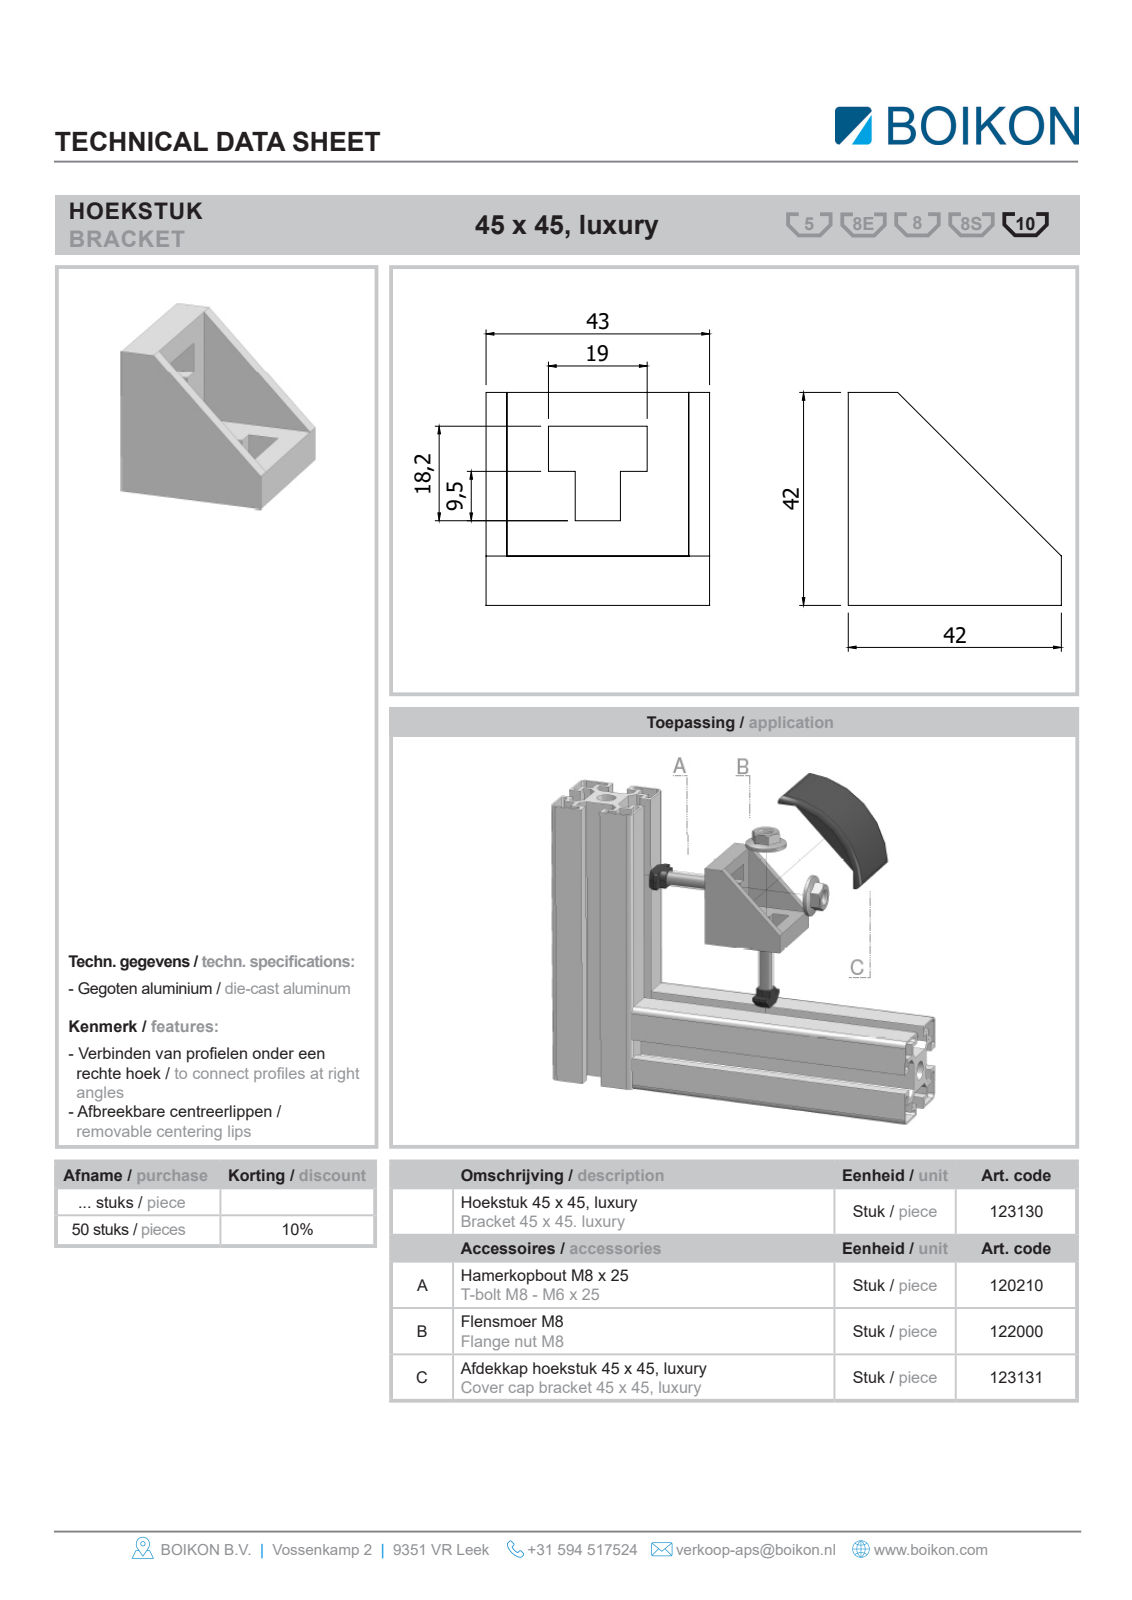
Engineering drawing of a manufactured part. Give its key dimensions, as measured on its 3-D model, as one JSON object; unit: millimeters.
{"part_name": "Root; 123130HOEKSTUK 45x45 LUXURYBOIKON0; 122000Flensmoer M8BOIKON; 120210Hamerkopbout M8x25BOIKON (+1 more)", "step_written_by": "HiCAD 2013 1802.4 Build 509 (AUTOMOTIVE_DESIGN)", "units": "millimeters", "bodies": {"solids": 6, "faces": 214, "planar": 161, "cylindrical": 29, "other": 24}, "overall_size": [56.59, 56.59, 43], "volume_mm3": 51750, "surface_area_mm2": 21848, "round_holes": [[8, 2]], "round_bosses_or_shafts": [[21, 2], [6.47, 2]], "partial_cylinders_radius": [[1, 8], [0.4, 4], [3, 2], [5, 2], [9.7, 2], [45, 1]], "face_to_face_distances": [9.5, 41, 31.5, 43, 4, 39, 35, 8, 8.7, 13.35]}
